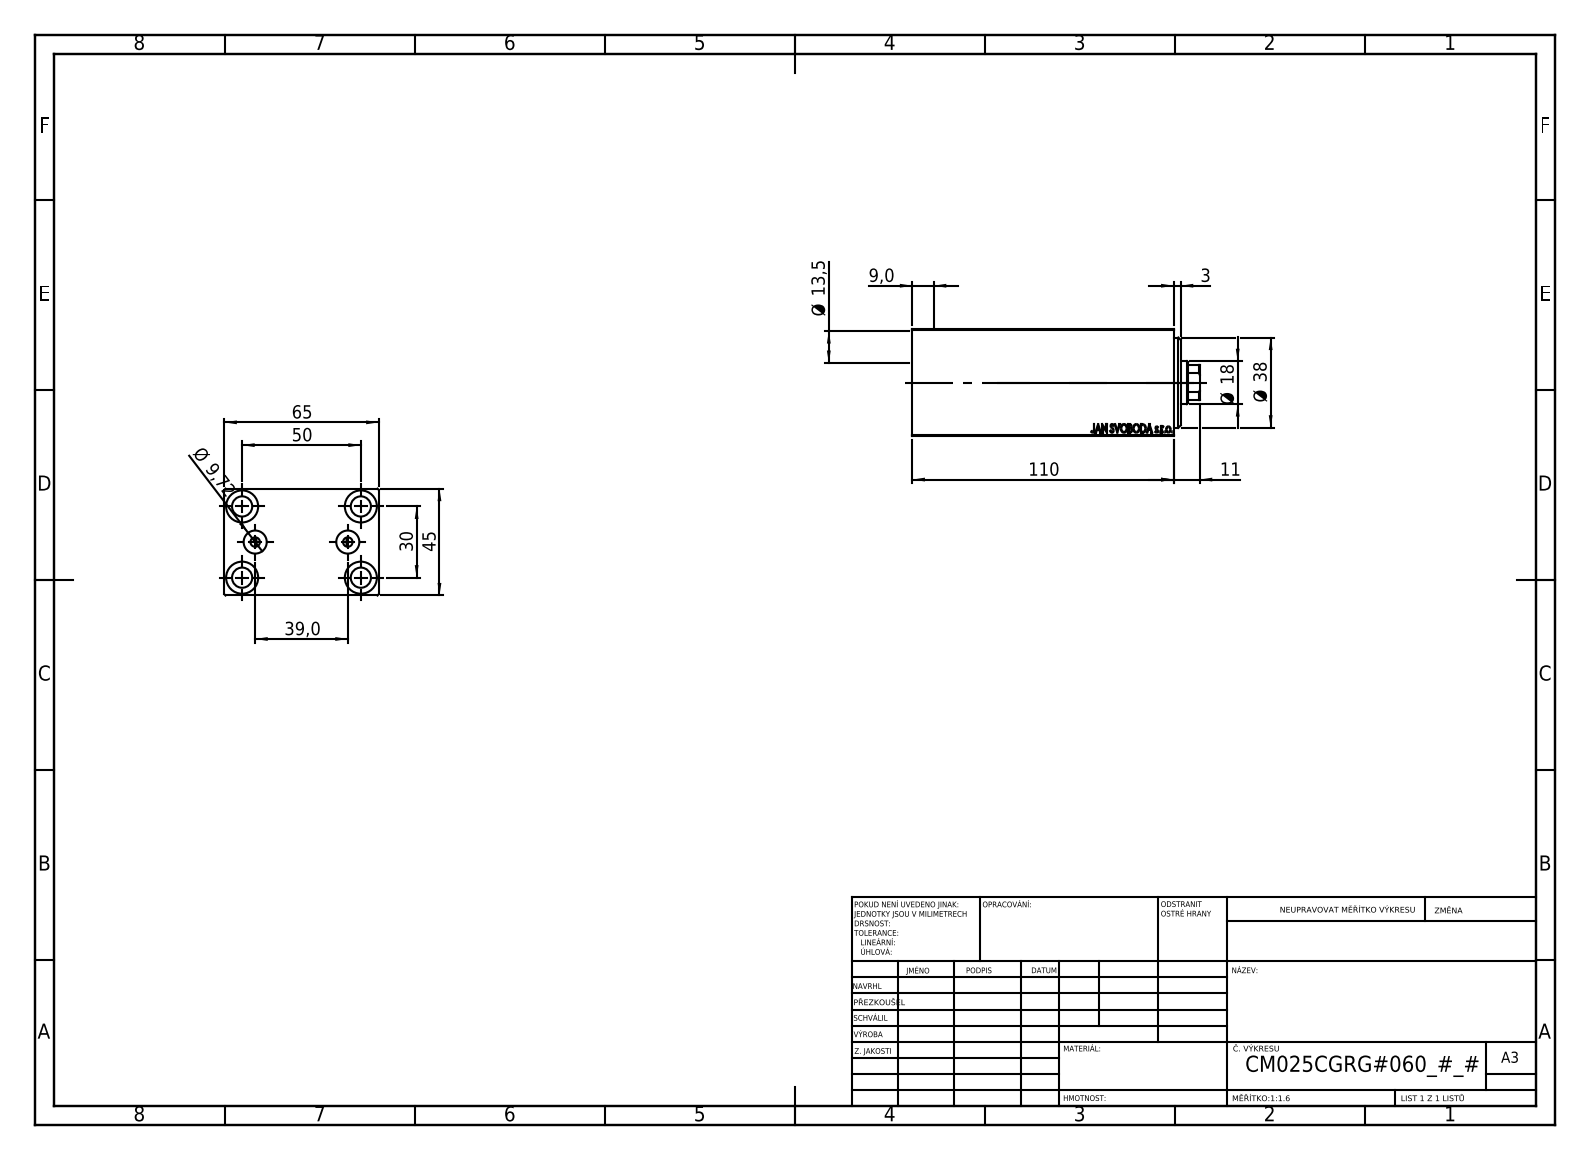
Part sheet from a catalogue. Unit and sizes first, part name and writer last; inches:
Units: inches
Overall size (bounding box): 4.764 × 2.559 × 1.772
Round holes (diameter × count): ⌀0.335 ×5, ⌀0.531 ×4, ⌀0.157 ×2, ⌀0.383 ×2, ⌀0.709 ×1, ⌀0.846 ×1, ⌀0.984 ×1, ⌀1.063 ×1, ⌀1.496 ×1
Partial cylindrical surfaces — rounded edges, fillets, slot ends (radius × count): R0.335 ×1
Main face-to-face distances: 1.772, 2.559, 0.236, 3.898, 4.094, 4.134, 0.197, 4.331, 0.118, 0.315
Hole centre spacings: 0.629, 1.148, 1.849, 0.768, 1.181, 1.969, 2.296, 1.535
Volume: 16.87 in³ · Surface area: 102.8 in²
Bodies: 3 solids, 858 faces (408 planar, 56 cylindrical, 394 other)
Part name (STEP PRODUCT): V450CM_C_Body; V450CM_C_VCP; V450CM_VC_B
STEP written by: SolidWorks 2019 (CONFIG_CONTROL_DESIGN)
